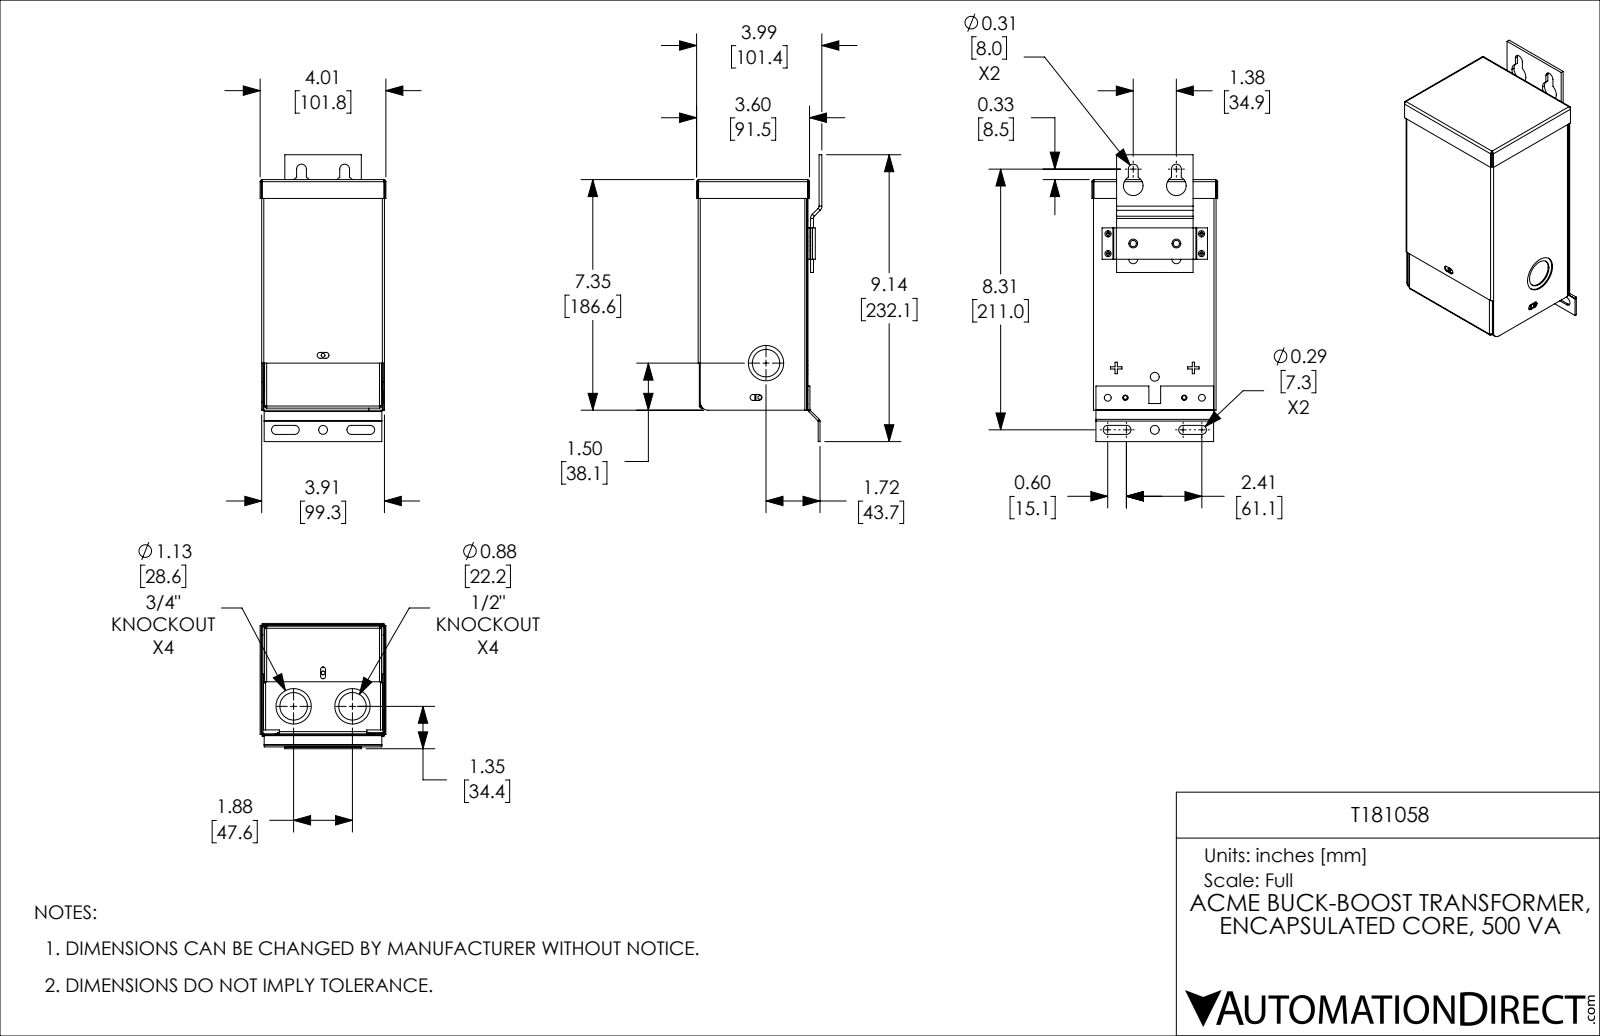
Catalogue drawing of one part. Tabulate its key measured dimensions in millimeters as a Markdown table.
| quantity | value |
| --- | --- |
| part name | T181058 |
| STEP written by | SolidWorks 2021 (CONFIG_CONTROL_DESIGN) |
| units | millimeters |
| bodies | 7 solids, 528 faces (326 planar, 154 cylindrical, 48 other) |
| overall size | 232.07 × 101.8 × 101.43 |
| volume | 113 073 mm³ |
| surface area | 227 401 mm² |
| round holes (diameter × count) | 3.05 × 5, 7.14 × 3, 7.14 × 3, 22.22 × 3, 28.57 × 3, 4.34 × 2, 4.76 × 2, 5.11 × 2, 5.54 × 2, 15.88 × 2, 28.58 × 1 |
| round bosses / shafts (diameter × count) | 30.4 × 3, 24.05 × 3 |
| partial cylindrical surfaces (radius × count) | 0.79 × 16, 1.7 × 16, 2.38 × 8, 0.66 × 4, 2.18 × 4, 3.66 × 4, 0.43 × 2, 1.96 × 2 |
| main face-to-face distances | 0.91, 87.99, 98.41, 87.08, 99.32, 97.5, 88.9, 1.53, 183.95, 182.42 |
| hole center spacings | 34.92, 12.7, 12.74, 14.27, 14.29, 29.09, 29.23, 34.94 |
